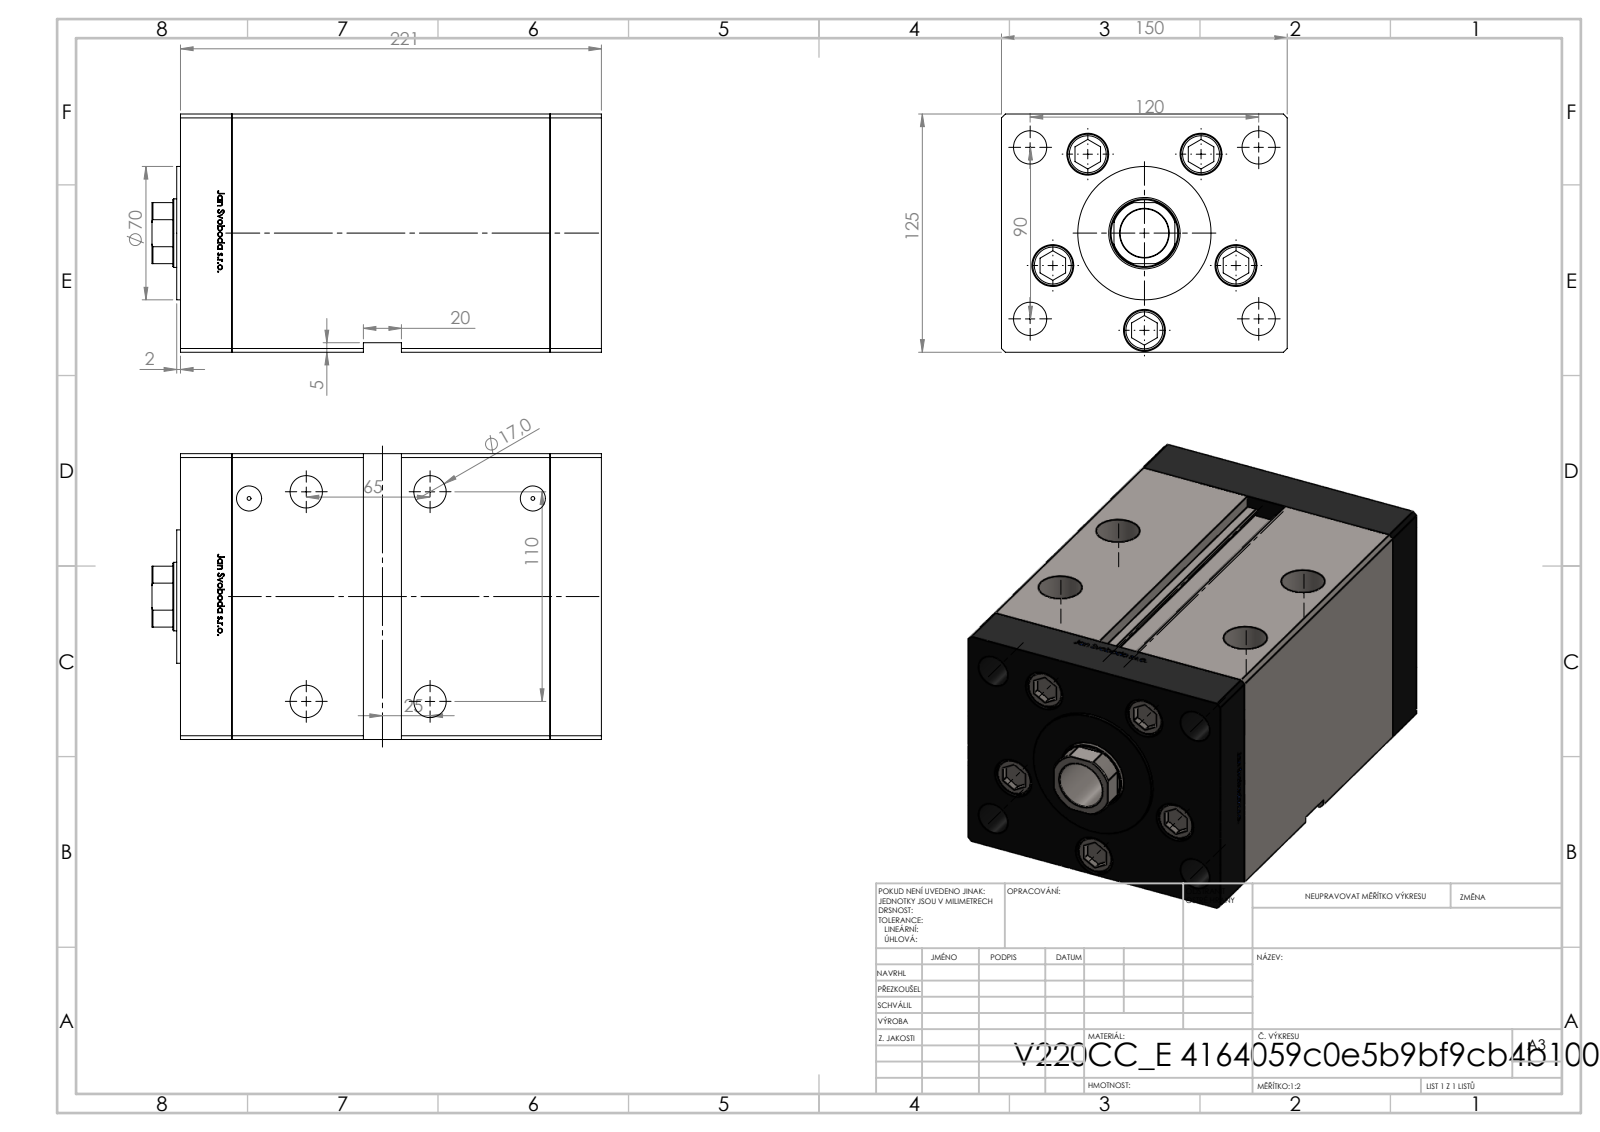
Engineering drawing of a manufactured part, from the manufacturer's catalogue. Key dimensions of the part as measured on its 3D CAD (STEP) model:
Part name (STEP PRODUCT): V220C_VC_E; V220C_E MIDDLE; V220C BACK_E; ALLEN BOLT (+1 more)
STEP written by: SolidWorks 2019 (CONFIG_CONTROL_DESIGN)
Units: millimetres
Bodies: 14 solids, 1214 faces (475 planar, 165 cylindrical, 574 other)
Overall size (bounding box): 236 × 150 × 125
Volume: 3 421 000 mm³ · Surface area: 396 942 mm²
Round holes (diameter × count): ⌀17.5 ×9, ⌀22 ×5, ⌀17 ×4, ⌀23 ×4, ⌀2 ×2, ⌀13.16 ×2, ⌀25.5 ×1, ⌀36 ×1, ⌀37.5 ×1
Round bosses / shafts (diameter × count): ⌀21 ×5, ⌀8 ×5, ⌀80 ×1, ⌀70 ×1
Partial cylindrical surfaces — rounded edges, fillets, slot ends (radius × count): R0.93 ×2, R17.5 ×1
Main face-to-face distances: 27, 194, 167, 125, 150, 33.5, 6.5, 221, 160.5, 187.5
Hole centre spacings: 51, 75, 30.43, 30.48, 58.89, 60.3, 61.25, 63.14
